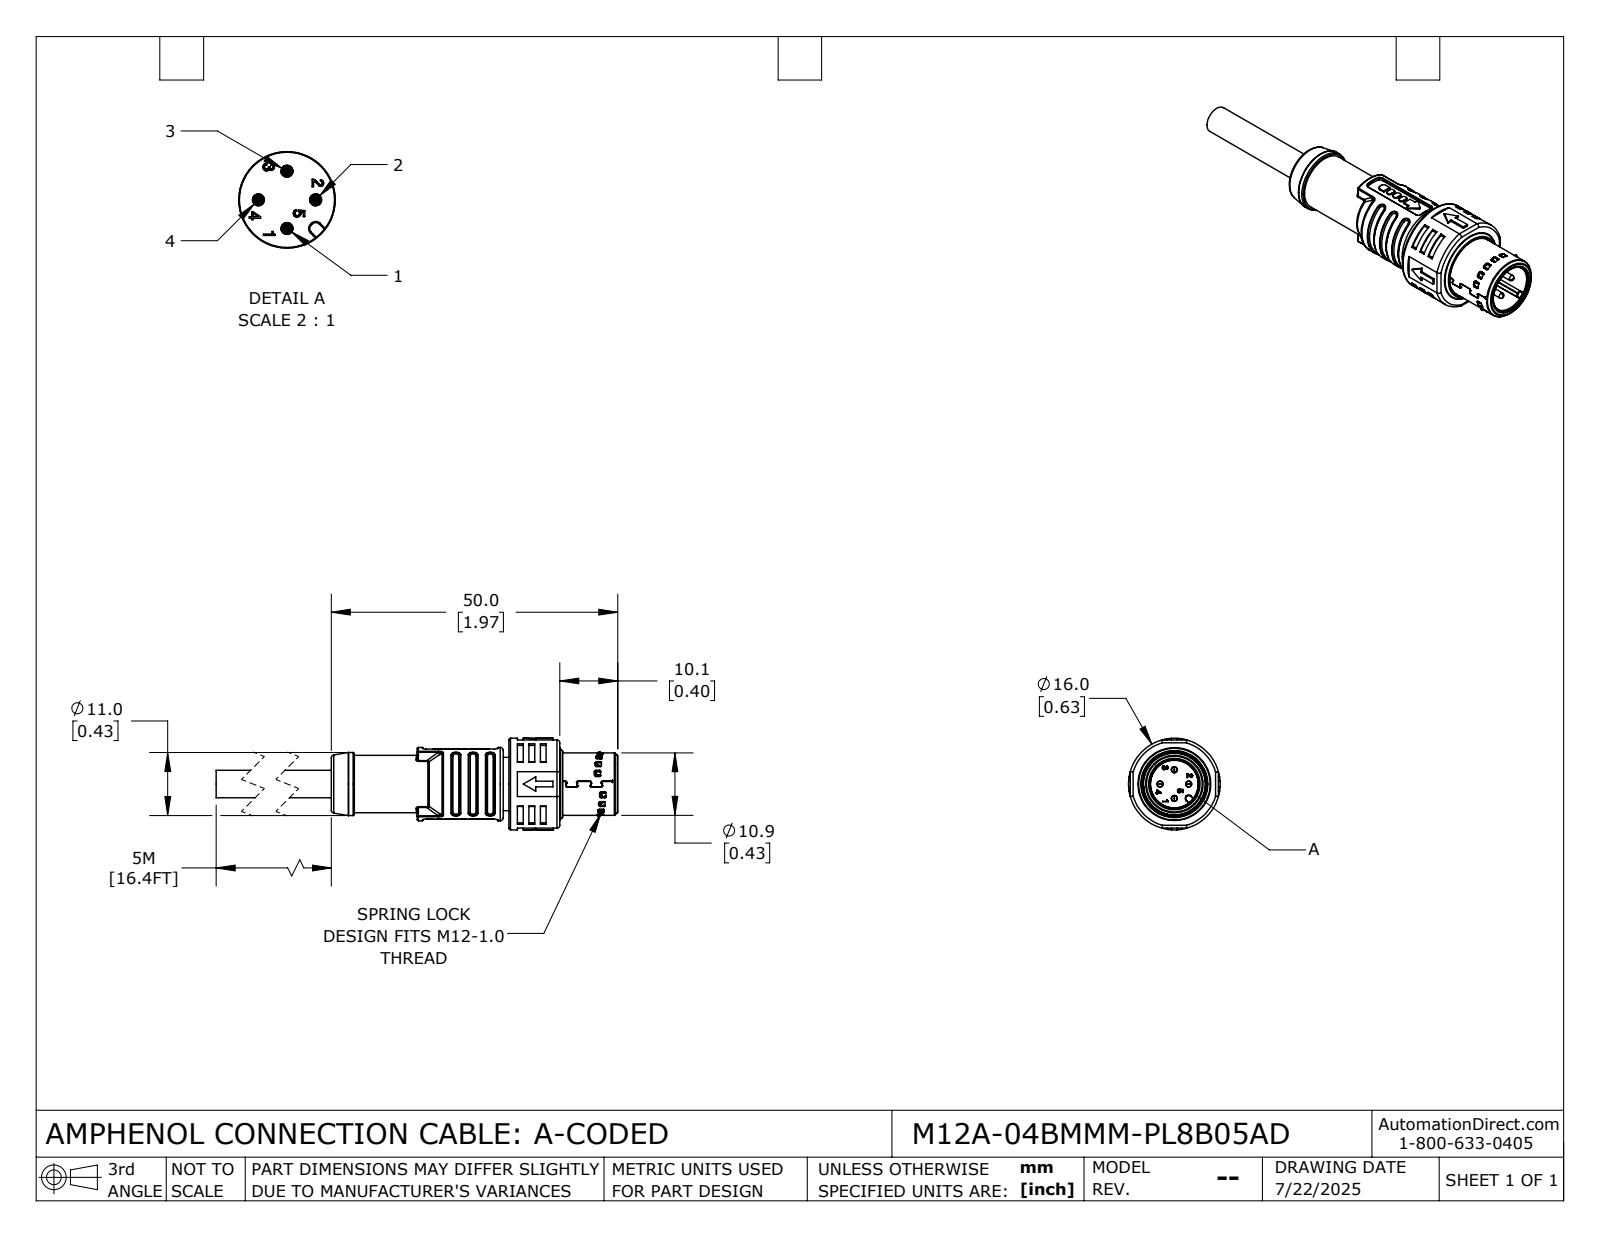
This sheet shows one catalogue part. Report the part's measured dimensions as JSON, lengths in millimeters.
{"part_name": "M12A-04BMMM-PL8B05AD", "step_written_by": "SolidWorks 2024 (CONFIG_CONTROL_DESIGN)", "units": "millimeters", "bodies": {"solids": 1, "faces": 2276, "planar": 1081, "cylindrical": 672, "other": 523}, "overall_size": [72.7, 16, 16], "volume_mm3": 5180, "surface_area_mm2": 5970, "round_holes": [[1, 4], [1.4, 4], [8.3, 1], [9, 1], [10.2, 1], [10.5, 1], [11.5, 1], [11.8, 1], [14.2, 1]], "round_bosses_or_shafts": [[1.4, 4], [1, 4], [16, 1], [14.1, 1], [12.8, 1], [12.4, 1], [11, 1], [10.9, 1]], "partial_cylinders_radius": [[0.2, 114], [0.3, 66], [0.3, 64], [0.2, 44], [0.5, 38], [0.1, 12], [0.7, 11], [0.1, 10]], "face_to_face_distances": [1, 10.1, 8.9, 8.6, 2.5, 1.5, 1.2, 32.5, 15.4, 41.1], "hole_center_spacings": [2.5, 3.5, 5]}
